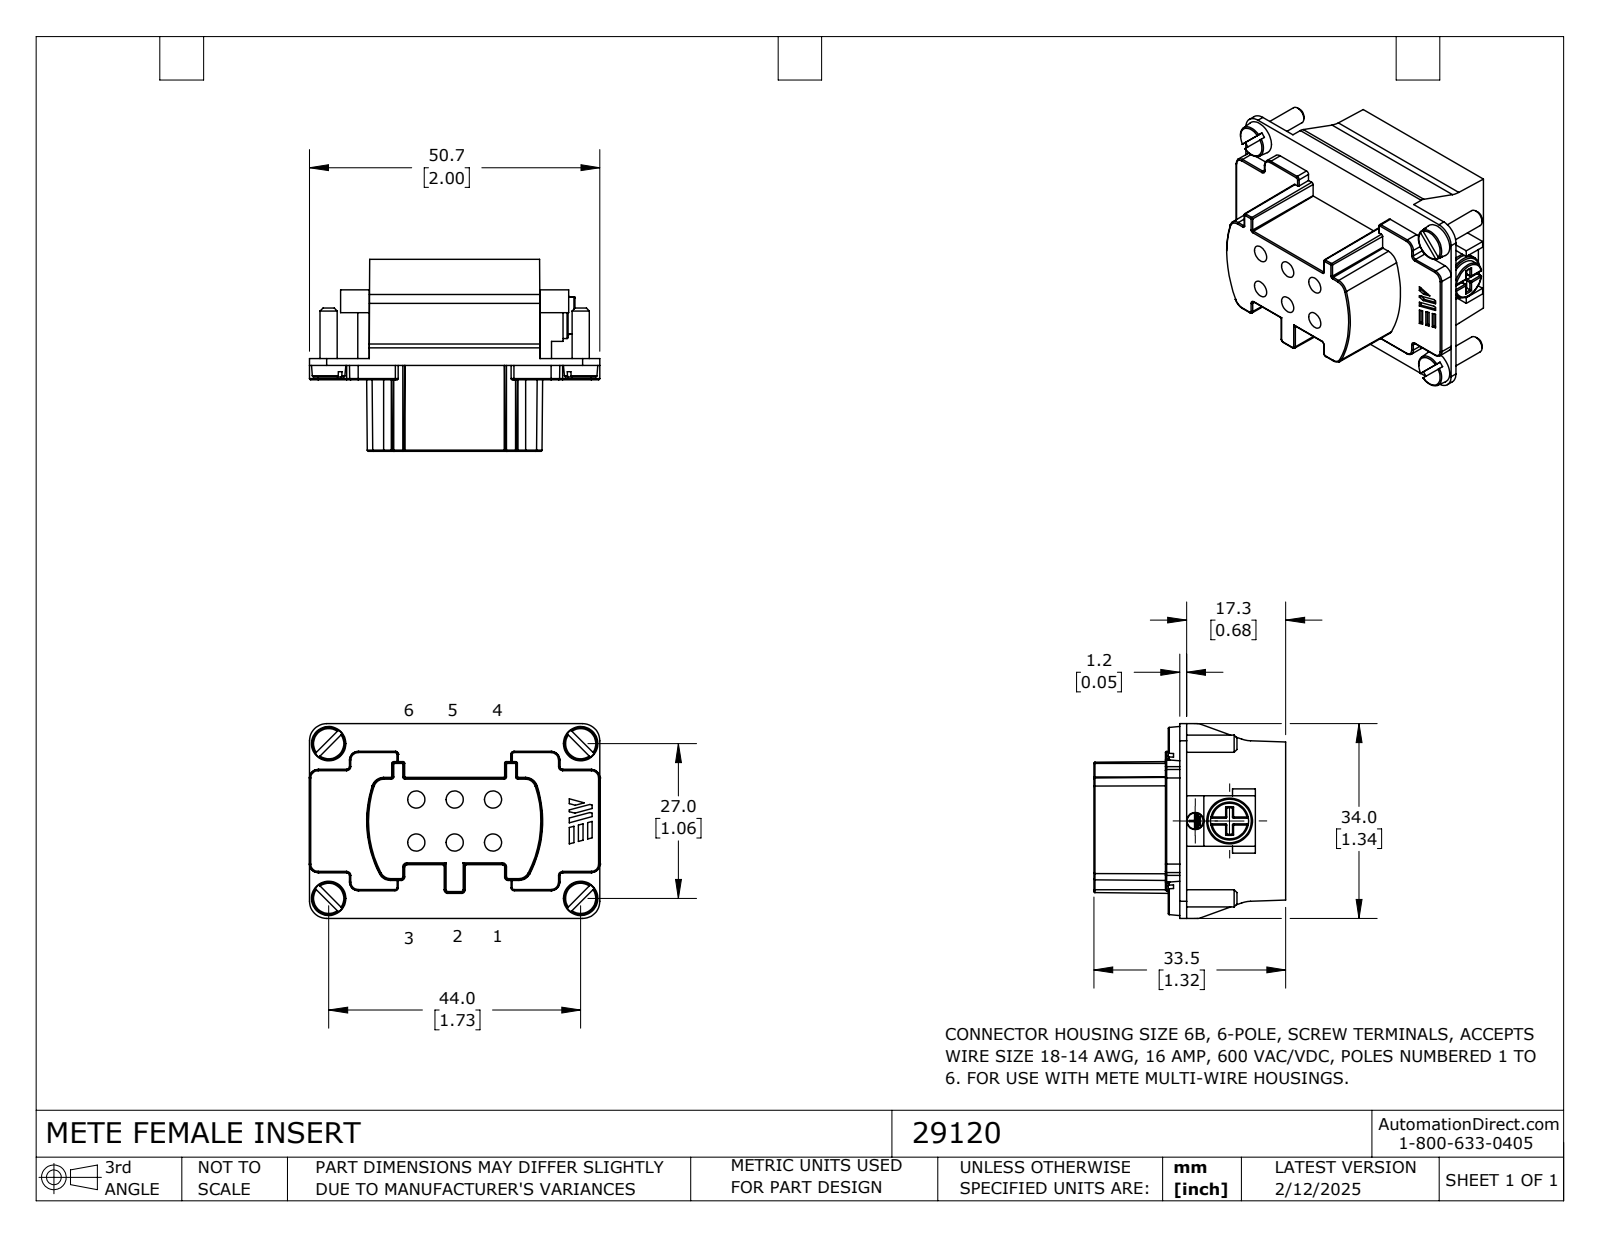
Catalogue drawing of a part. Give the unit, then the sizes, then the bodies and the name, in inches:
Units: inches
Overall size (bounding box): 1.996 × 1.339 × 1.319
Round holes (diameter × count): ⌀0.118 ×7
Round bosses / shafts (diameter × count): ⌀0.118 ×4, ⌀0.315 ×1, ⌀0.261 ×1, ⌀0.11 ×1
Partial cylindrical surfaces — rounded edges, fillets, slot ends (radius × count): R0.008 ×37, R0.118 ×4, R0.02 ×2, R0.079 ×2, R0.197 ×2, R0.091 ×1
Main face-to-face distances: 0.047, 0.681, 0.728, 0.098, 0.146, 0.827, 0.492, 0.638, 1.319, 0.591
Hole centre spacings: 0.264, 0.396, 0.295, 0.528, 0.605
Volume: 1.59 in³ · Surface area: 16.22 in²
Bodies: 1 solid, 383 faces (172 planar, 95 cylindrical, 116 other)
Part name (STEP PRODUCT): 29120
STEP written by: SolidWorks 2024 (CONFIG_CONTROL_DESIGN)
